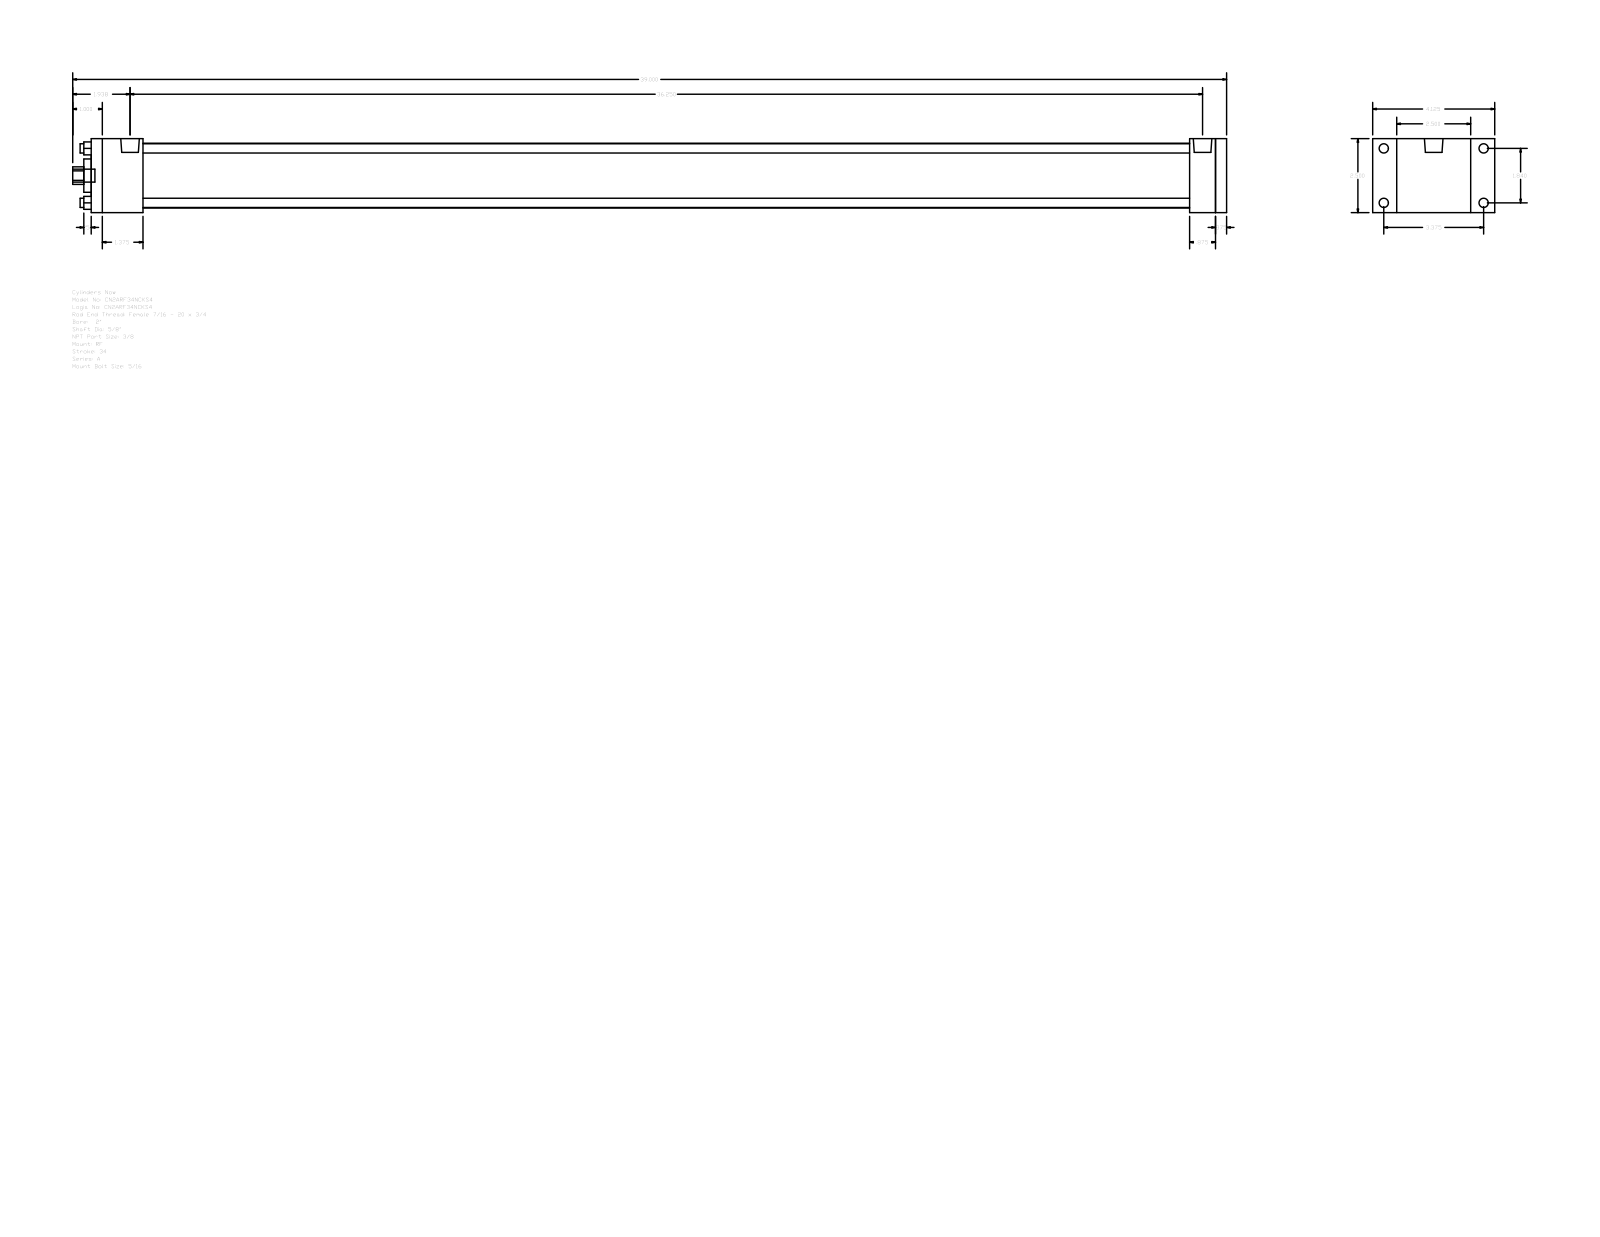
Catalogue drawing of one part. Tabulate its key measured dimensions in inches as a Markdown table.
| quantity | value |
| --- | --- |
| part name | A_RF__0200_0.625 |
| STEP written by | GSSL Pune (CONFIG_CONTROL_DESIGN) |
| units | inches |
| bodies | 0 solids, 92 faces (64 planar, 28 cylindrical, 0 other) |
| overall size | 39 × 4.125 × 2.5 |
| round holes (diameter × count) | 0.313 × 4, 0.625 × 1, 1.125 × 1, 2.19 × 1 |
| round bosses / shafts (diameter × count) | 0.313 × 4, 0.219 × 4, 0.627 × 2, 0.437 × 1 |
| partial cylindrical surfaces (radius × count) | 0.297 × 1 |
| main face-to-face distances | 2.5, 38.375, 0.375, 38, 1.75, 36.25, 36.625, 37.125, 35.375, 0.875 |
| hole center spacings | 1.301, 1.84, 2.602 |
